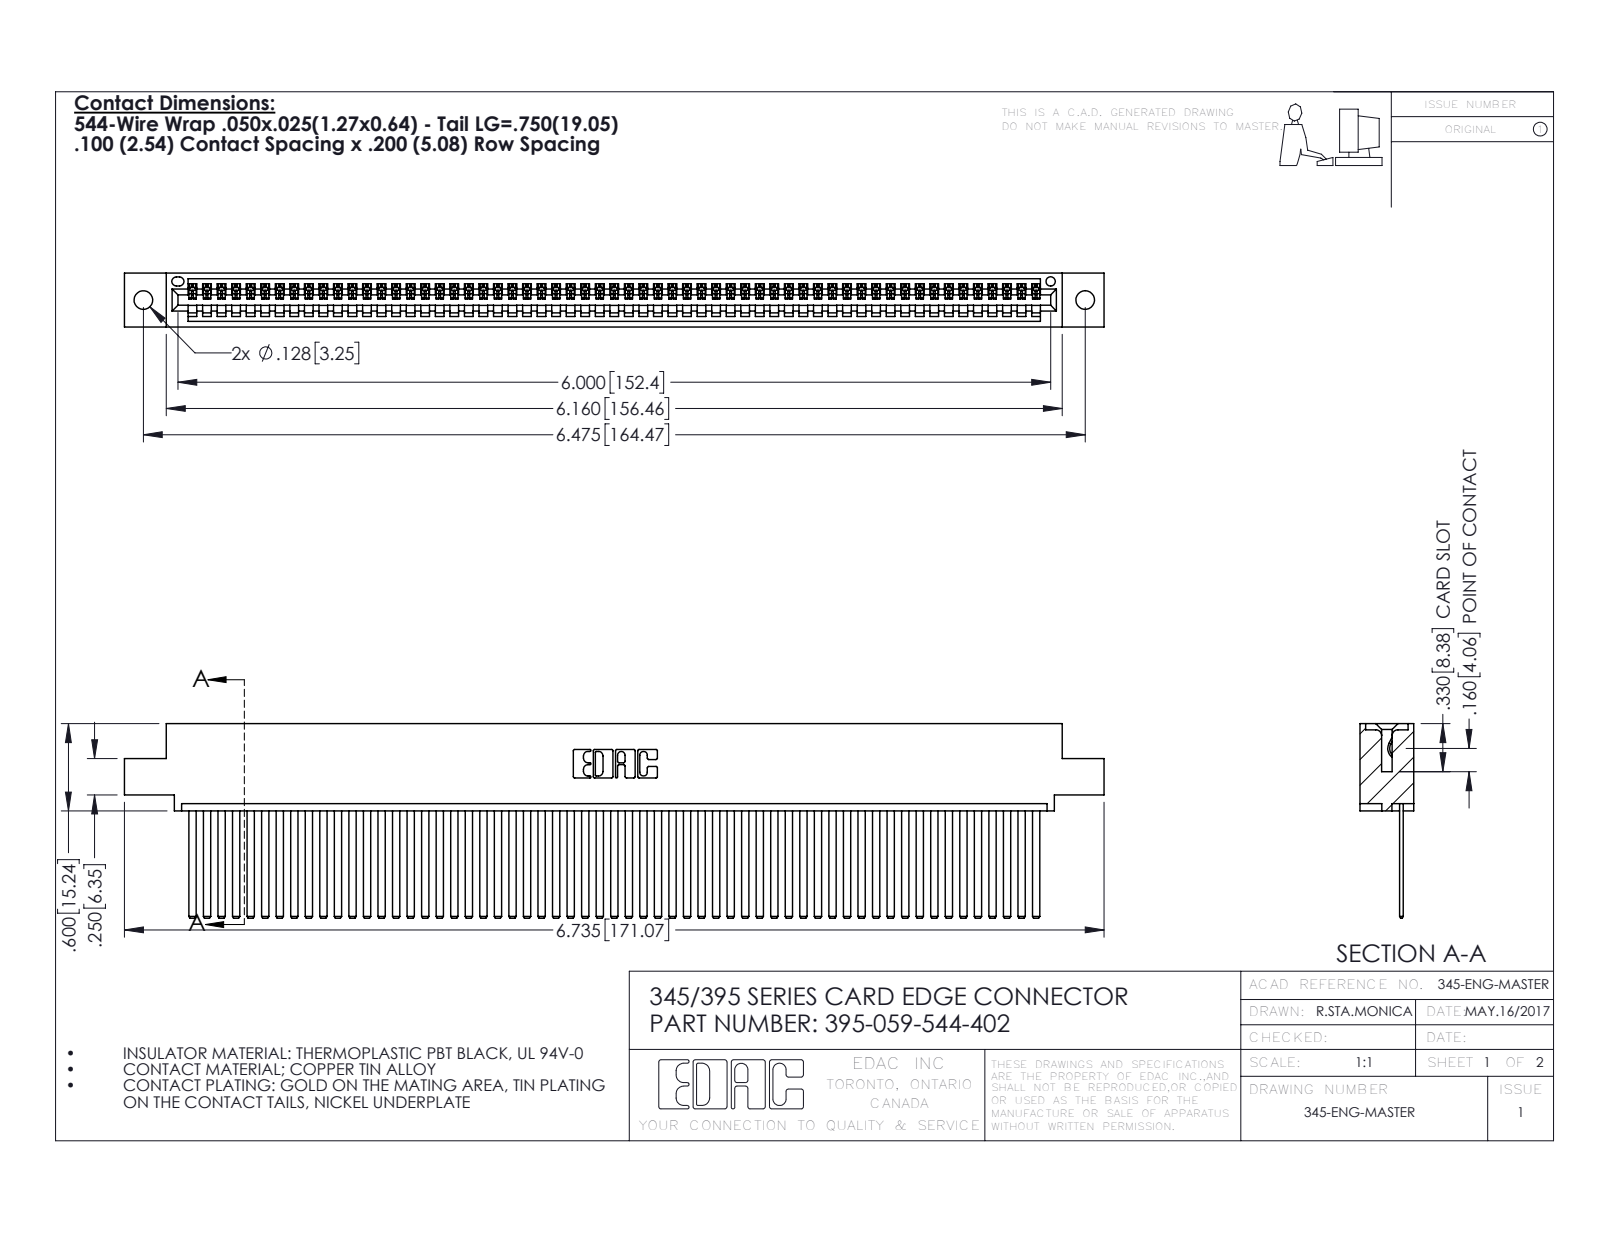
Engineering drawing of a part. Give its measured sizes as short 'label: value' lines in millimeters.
name: 345-292-001_345-293-144; 345 Part_0.110 Offset - 0.128 Dia; 395-059-544-402
written by: SolidWorks 2016 (CONFIG_CONTROL_DESIGN)
unit: mm
bodies: 60 solids, 3198 faces (2208 planar, 990 cylindrical, 0 other)
size: 171.1 × 34 × 9.4
volume: 16 960 mm³; area: 24 630 mm²
holes: 2× ⌀3.3, 1× ⌀1.6
rounds: 118× R0.2, 22× R0.3, 6× R0.2, 6× R0.8, 3× R0.7, 2× R0.8, 2× R1, 1× R0.4
face distances: 1.8, 7.6, 0.6, 2.5, 6.9, 9.4, 5.1, 5.7, 3.8, 1.8
hole spacings: 6.9, 158.5, 164.5
